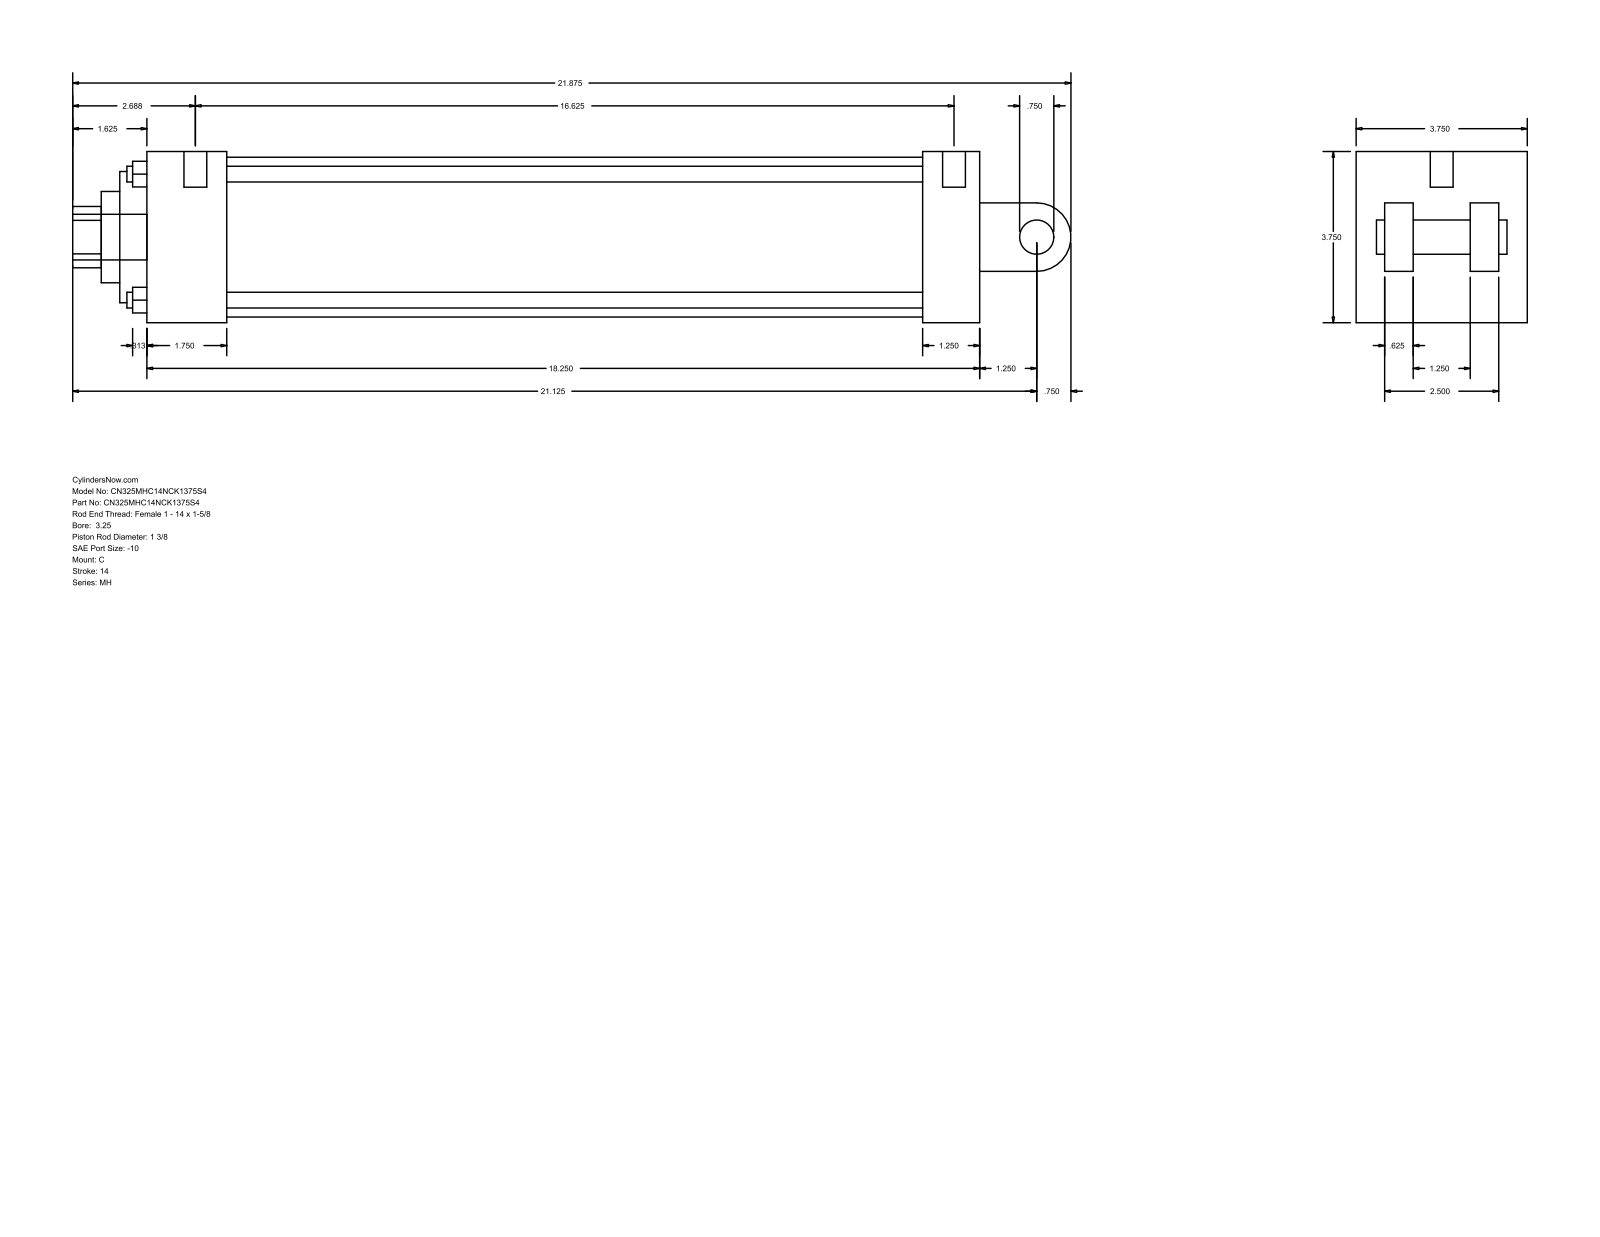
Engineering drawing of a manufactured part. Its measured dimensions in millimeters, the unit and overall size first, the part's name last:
Units: millimetres
Overall size (bounding box): 555.62 × 95.25 × 95.25
Round holes (diameter × count): ⌀8.76 ×4, ⌀5.56 ×2, ⌀12.7 ×1, ⌀34.92 ×1, ⌀50.8 ×1, ⌀73.03 ×1, ⌀88.9 ×1
Round bosses / shafts (diameter × count): ⌀5.56 ×2, ⌀25.4 ×1, ⌀19.05 ×1, ⌀12.7 ×1
Partial cylindrical surfaces — rounded edges, fillets, slot ends (radius × count): R17.06 ×1, R19.05 ×1
Main face-to-face distances: 95.24, 15.87, 463.55, 63.5, 31.74, 79.37, 47.63, 44.45, 431.8, 387.35
Hole centre spacings: 49.57, 70.1, 99.14, 4.76
Bodies: 0 solids, 101 faces (71 planar, 30 cylindrical, 0 other)
Part name (STEP PRODUCT): MH_C__0325_1.375
STEP written by: GSSL Pune (CONFIG_CONTROL_DESIGN)
